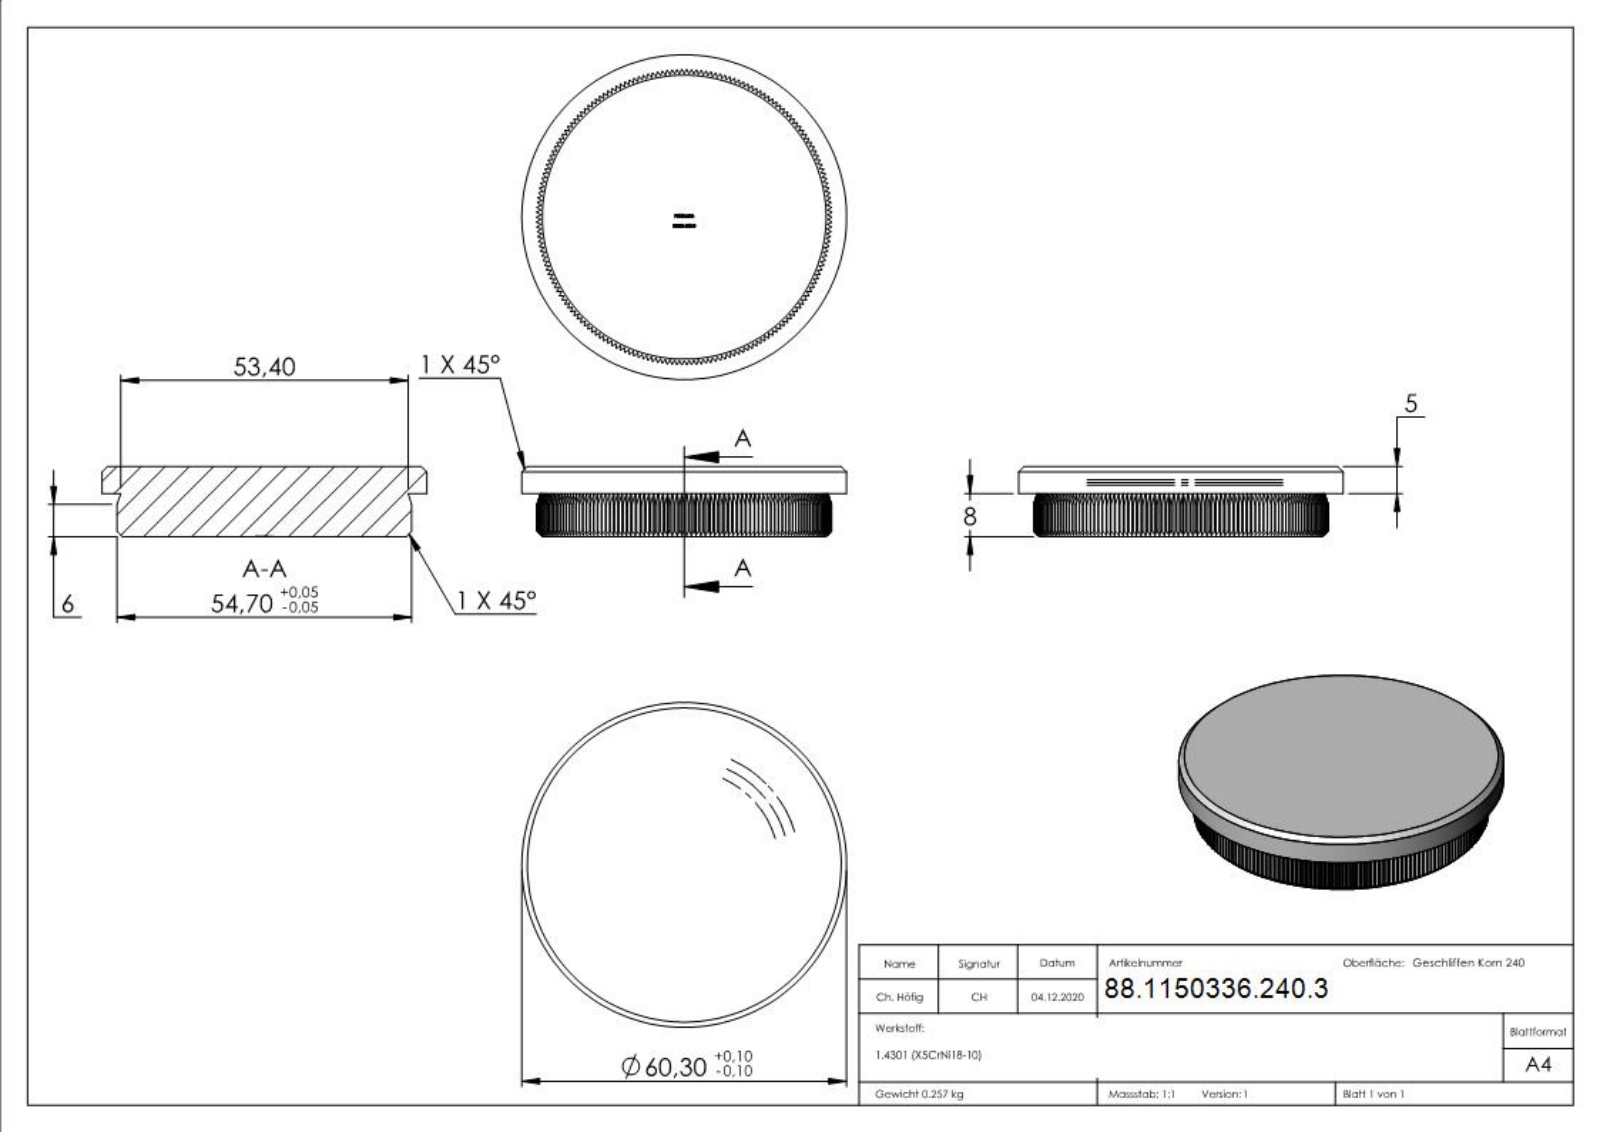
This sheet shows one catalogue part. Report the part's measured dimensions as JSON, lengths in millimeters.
{"part_name": "50336-240-3", "step_written_by": "SolidWorks 2018 (CONFIG_CONTROL_DESIGN)", "units": "millimeters", "bodies": {"solids": 1, "faces": 1025, "planar": 508, "cylindrical": 192, "other": 325}, "overall_size": [60.3, 60.3, 13], "volume_mm3": 32470, "surface_area_mm2": 8899, "round_bosses_or_shafts": [[60.3, 1]], "partial_cylinders_radius": [[27.35, 1]], "face_to_face_distances": [13, 8, 5, 26.64, 26.66, 26.62, 26.68, 7.9, 12.9, 1.79]}
